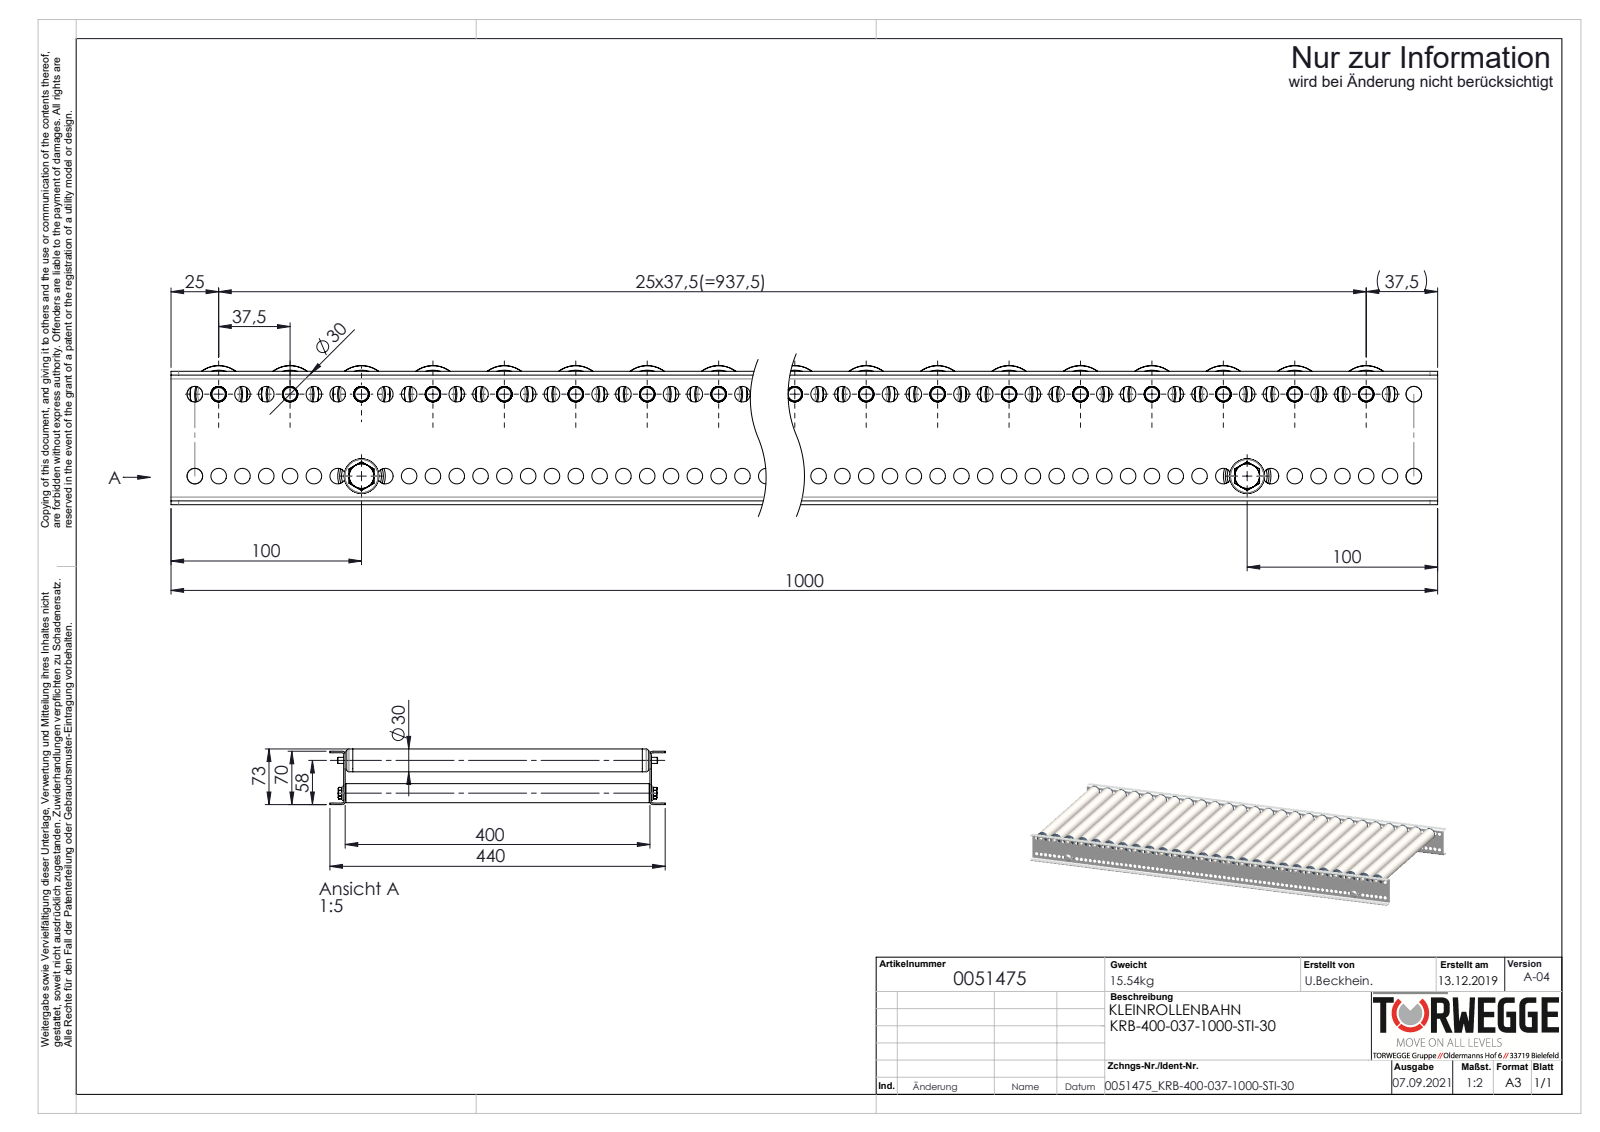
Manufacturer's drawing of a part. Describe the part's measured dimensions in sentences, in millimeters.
The part is named "S100994_Sperrzahnschraube_M08x16-8.8-A2K; 0039768_Tragrollenrohr-Ø30x1,5STI_KFG_0039768_L=380; 0040250_DRUCK-FEDER-8mm; 0024176_Passscheibe_DIN988_8x14x1 (+6 more)". Its 3-D file was written by "SolidWorks 2020 (AUTOMOTIVE_DESIGN)". It is 168 solids with 6996 faces: 2200 planar, 2768 cylindrical and 2028 other. Overall it measures 1000 by 440 by 73 millimeters. Its volume is 2 415 000 cubic millimeters and its surface area 2 952 000 square millimeters. Round holes: 158 of diameter 8.2, 26 of diameter 8, 26 of diameter 8.1, 26 of diameter 23.2, 26 of diameter 25.2, 26 of diameter 27, 2 of diameter 6.8, 2 of diameter 21. Round bosses or shafts: 26 of diameter 30, 26 of diameter 29.9, 26 of diameter 27.1, 26 of diameter 26.8, 26 of diameter 24, 26 of diameter 14, 2 of diameter 25, 2 of diameter 8. Partial cylindrical surfaces (rounded edges, fillets, slot ends): 26 of radius 5.05, 8 of radius 4, 4 of radius 2. The main face-to-face distances are 2, 402, 400, 68, 404, 66, 70, 10, 390, 20. The hole center spacings are 12.5, 25, 37.5, 50, 62.5, 75, 87.5, 100.
